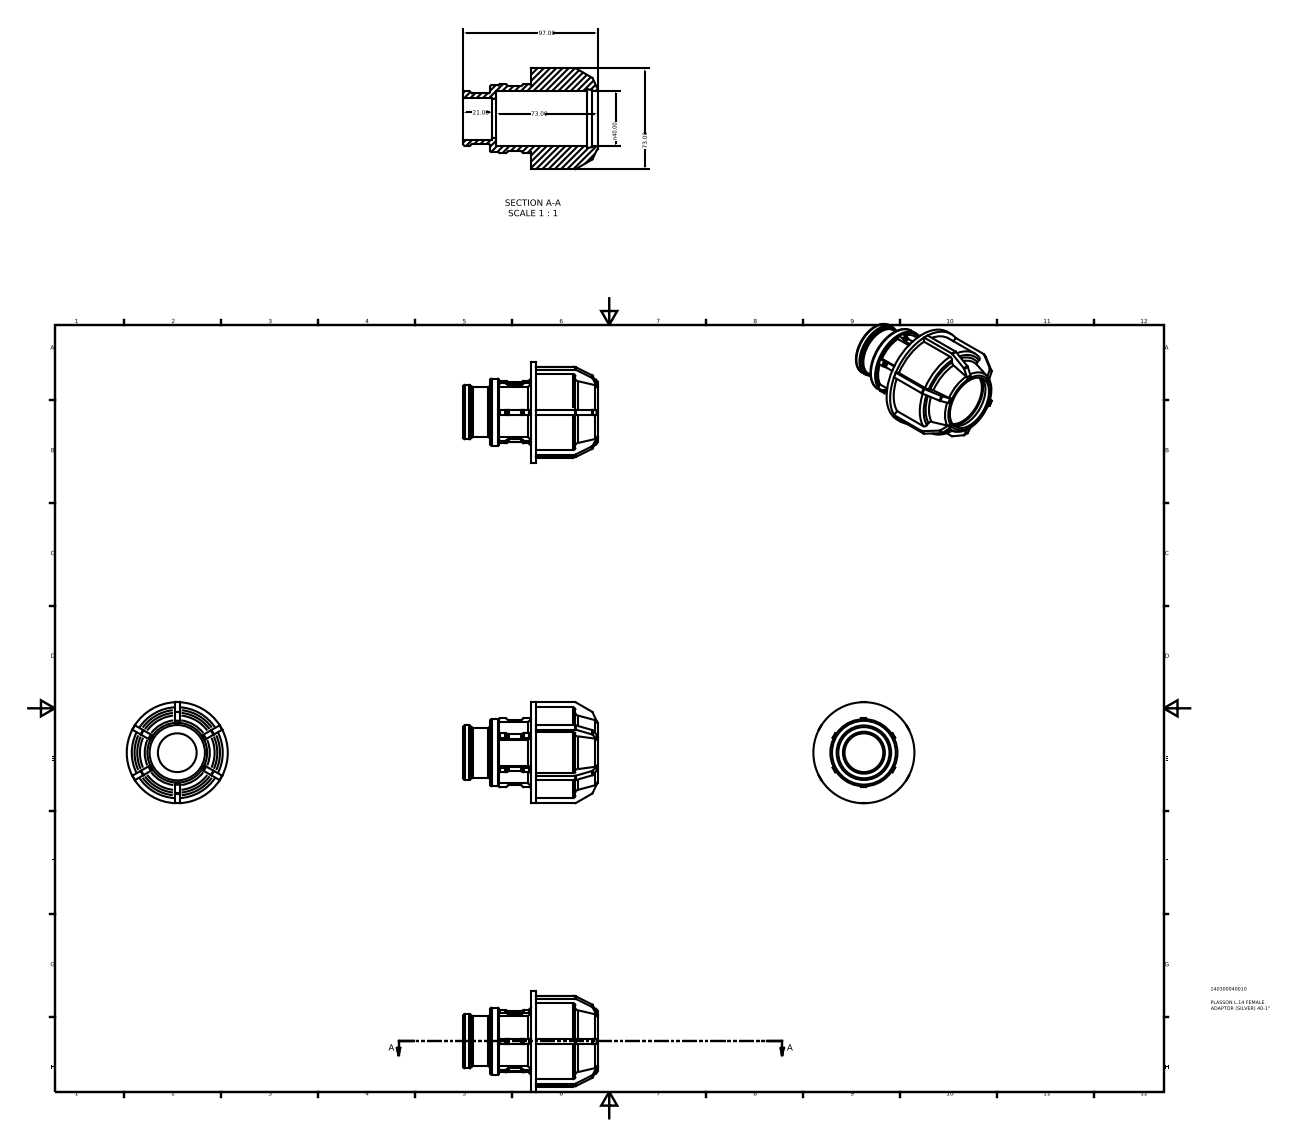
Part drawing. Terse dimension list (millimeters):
name: 140300040010
written by: Autodesk Inventor 2015 (AUTOMOTIVE_DESIGN)
unit: mm
bodies: 1 solid, 261 faces (159 planar, 68 cylindrical, 34 other)
size: 97 × 73 × 73
volume: 108 569 mm³; area: 37 084 mm²
holes: 1× ⌀28, 1× ⌀30.29, 1× ⌀40
bosses: 1× ⌀73, 1× ⌀65.7, 1× ⌀48.47, 1× ⌀43.92, 1× ⌀39.38, 1× ⌀36.35
rounds: 48× R1.2
face distances: 3.65, 3.64, 24.82, 28.47, 4.65, 73, 3.66, 29.47, 33.12, 19.35
